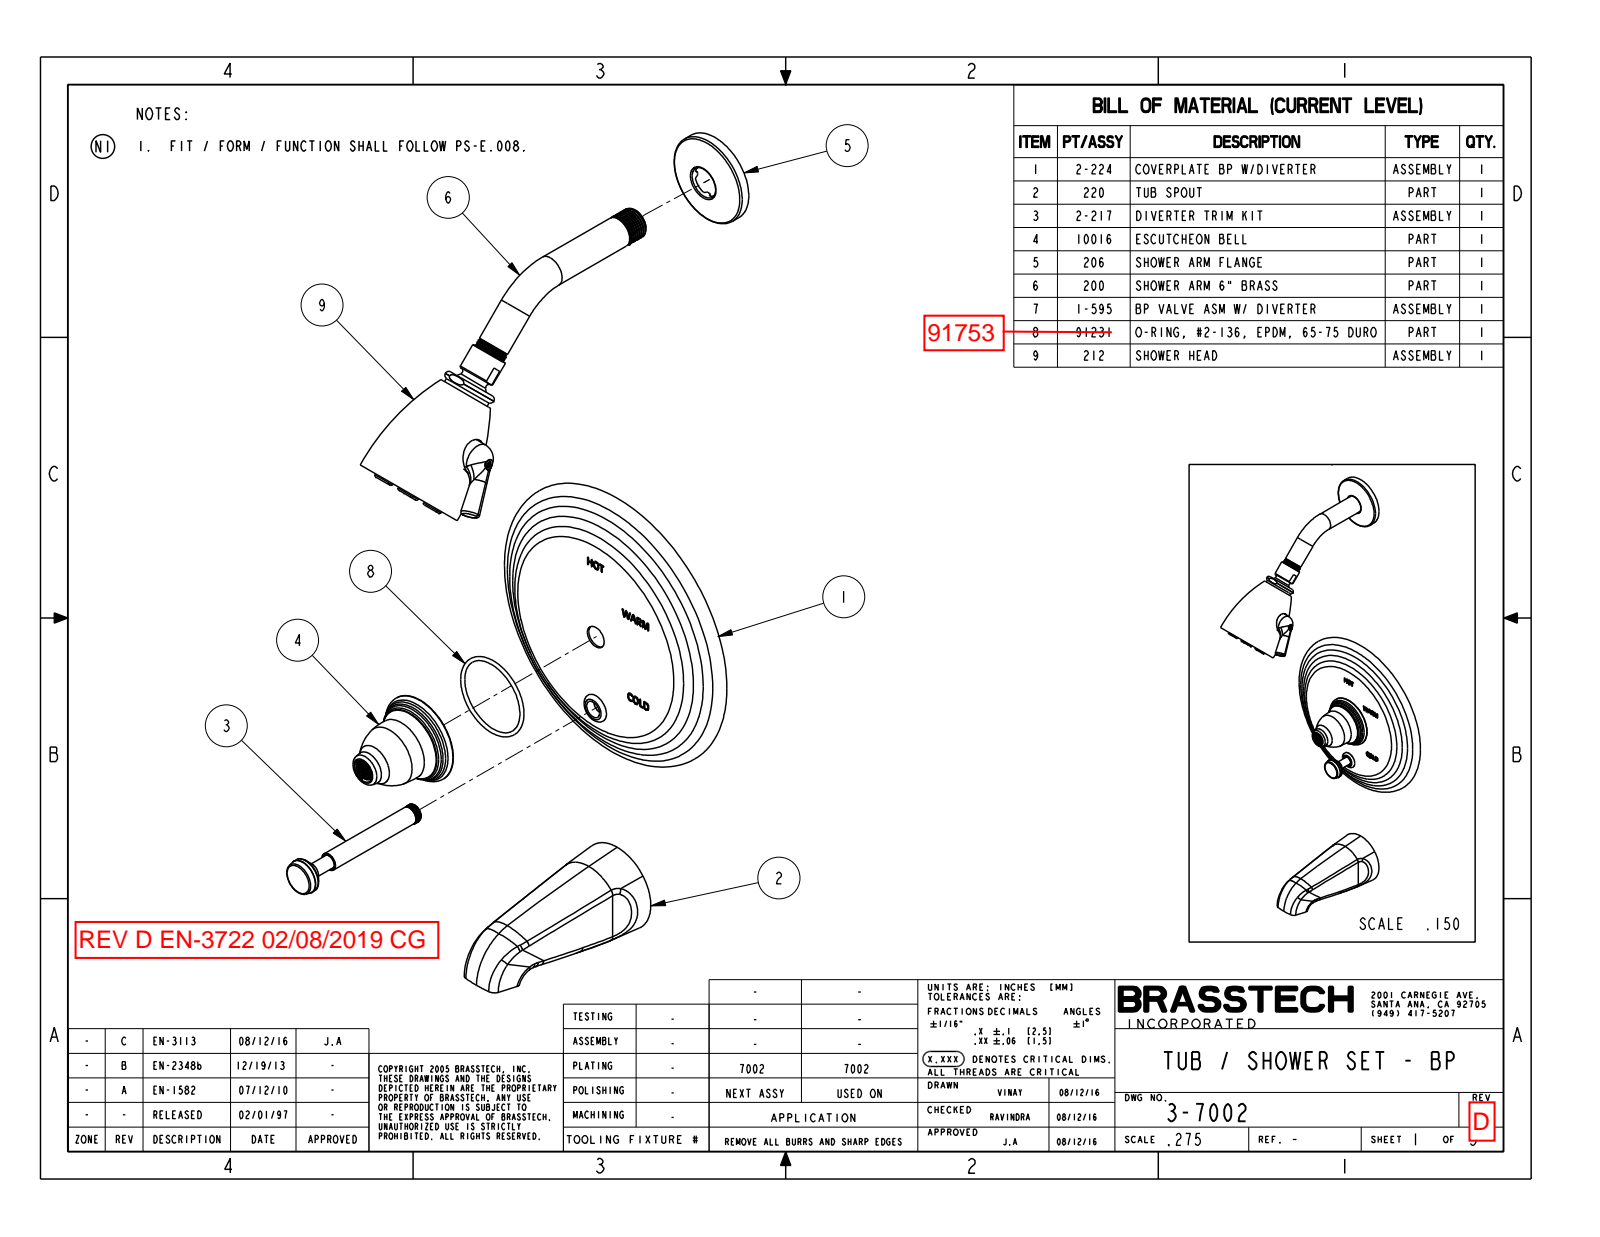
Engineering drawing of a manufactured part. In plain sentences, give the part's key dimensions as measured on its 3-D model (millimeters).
The part is named "3-7002_WEB". Its 3-D file was written by "PRO/ENGINEER BY PARAMETRIC TECHNOLOGY CORPORATION, 2009300 (CONFIG_CONTROL_DESIGN)". It is 8 solids with 2705 faces: 1137 planar, 832 cylindrical and 736 other. Overall it measures 568.4 by 264.3 by 196.9 millimeters. Its volume is 230 400 cubic millimeters and its surface area 296 800 square millimeters. Round holes: 8 of diameter 12.7, 2 of diameter 17.4, 1 of diameter 2.5, 1 of diameter 3.8, 1 of diameter 4, 1 of diameter 4.2, 1 of diameter 4.7, 1 of diameter 5.1, 1 of diameter 5.2, 1 of diameter 6, 1 of diameter 6.7, 1 of diameter 8.1. Round bosses or shafts: 6 of diameter 7.6, 6 of diameter 5.7, 6 of diameter 2.5, 2 of diameter 20.7, 1 of diameter 60.5, 1 of diameter 59.4, 1 of diameter 52.3, 1 of diameter 31. Partial cylindrical surfaces (rounded edges, fillets, slot ends): 8 of radius 0.2, 6 of radius 0.2, 6 of radius 6.4, 4 of radius 0.3, 4 of radius 0.4, 4 of radius 0.8, 4 of radius 2.9, 4 of radius 4.9. The main face-to-face distances are 1.3, 7.2, 17.9, 19.2, 2.5, 9.8, 102, 84.1, 82.8, 48.8. The hole center spacings are 20.3, 35.2, 40.6, 35.2, 55.2, 148, 203.2, 304.8.
